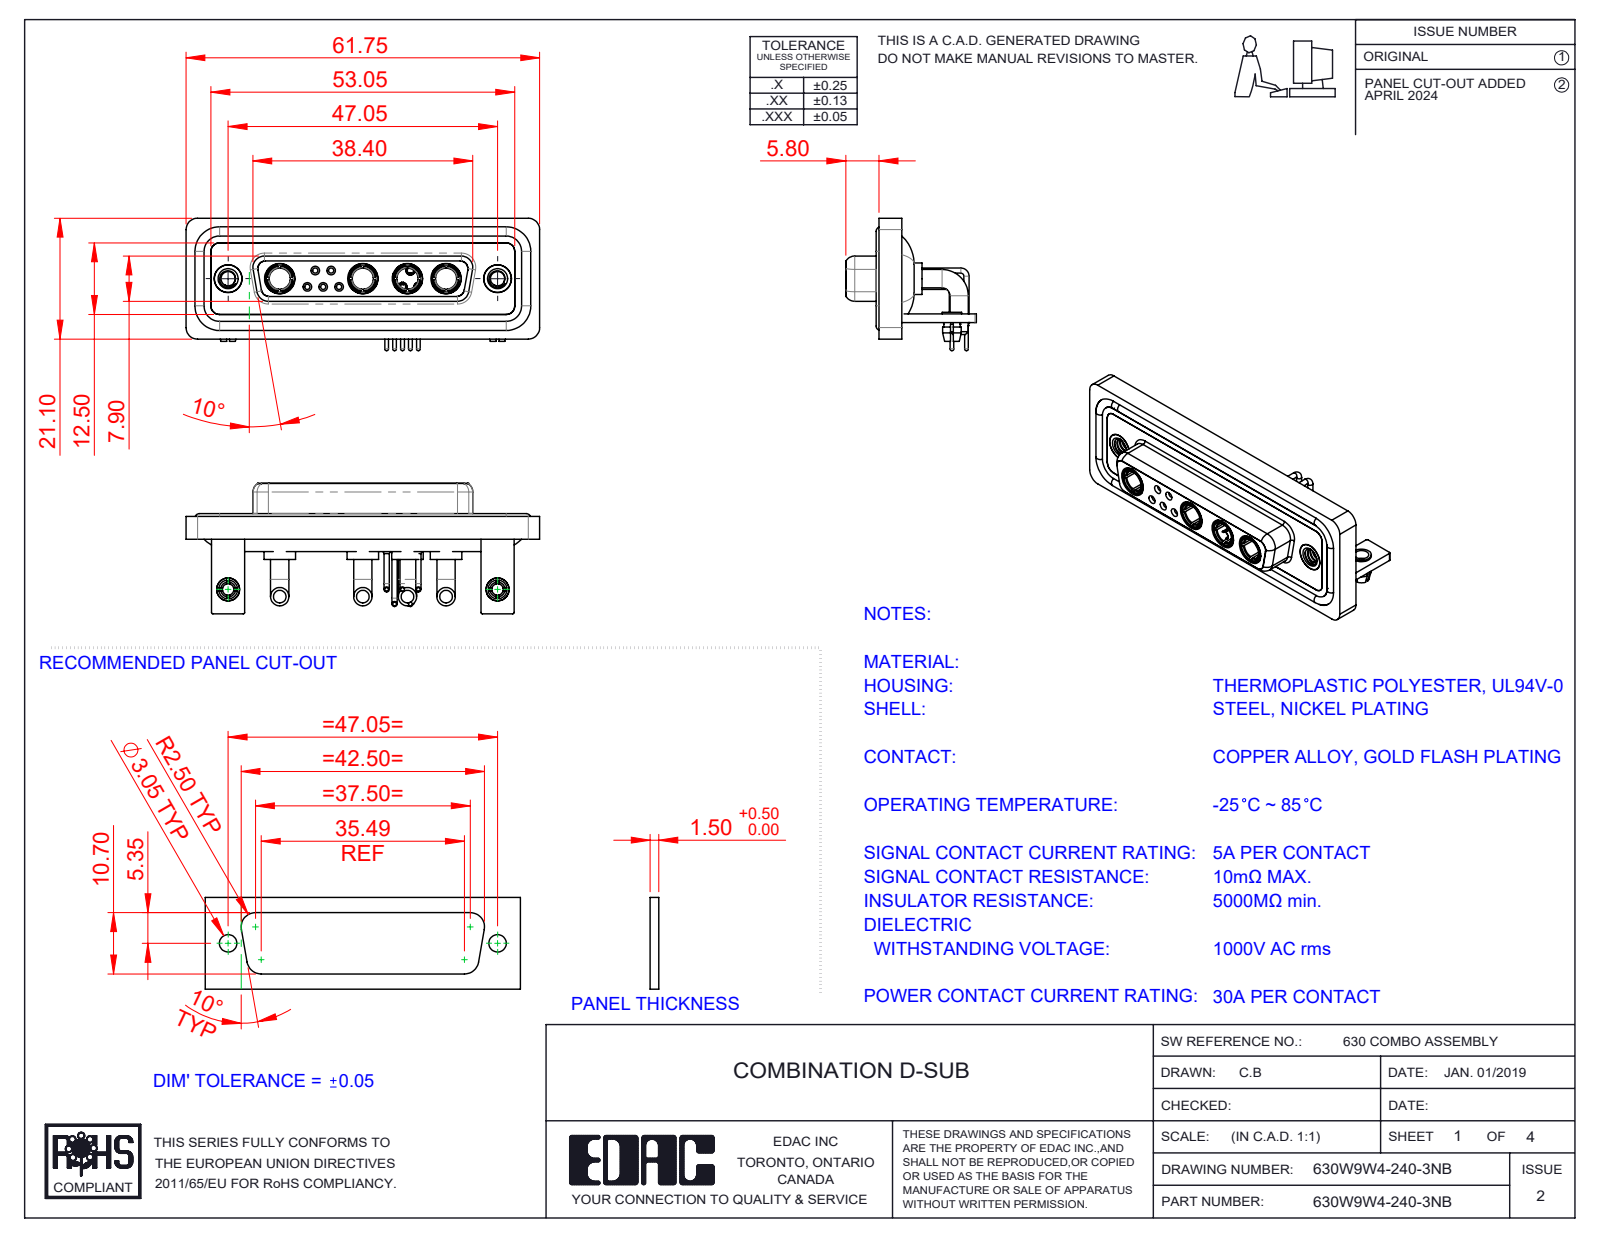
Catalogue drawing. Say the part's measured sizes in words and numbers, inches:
The part is named "Power Socket_30A RA; 630Combo Stabilizer Bracket_50 Contacts; 630Combo Shell Rear_25 Contacts; 630Combo Board Lock_50 Contacts (+7 more)". Its 3-D file was written by "SolidWorks 2023 (CONFIG_CONTROL_DESIGN)". It is 24 solids with 1097 faces: 364 planar, 457 cylindrical and 276 other. Overall it measures 2.431 by 0.91 by 0.898 inches. Its volume is 0.547 cubic inches and its surface area 23.36 square inches. Round holes: 7 of diameter 0.079, 6 of diameter 0.191, 5 of diameter 0.035, 5 of diameter 0.043, 5 of diameter 0.059, 4 of diameter 0.098, 4 of diameter 0.146, 4 of diameter 0.209, 3 of diameter 0.063, 2 of diameter 0.067, 2 of diameter 0.126, 2 of diameter 0.157. Round bosses or shafts: 10 of diameter 0.035, 9 of diameter 0.063, 8 of diameter 0.126, 5 of diameter 0.079, 5 of diameter 0.059, 5 of diameter 0.026, 4 of diameter 0.217, 4 of diameter 0.205. Partial cylindrical surfaces (rounded edges, fillets, slot ends): 19 of radius 0.079, 18 of radius 0.059, 16 of radius 0.01, 8 of radius 0.053, 8 of radius 0.063, 5 of radius 0.02, 4 of radius 0.024, 4 of radius 0.026. The main face-to-face distances are 0.016, 0.071, 0.114, 0.146, 0.059, 0.161, 0.043, 0.055, 0.063, 0.098. The hole center spacings are 0.124, 0.109, 0.198, 0.545, 0.436, 0.504, 0.61, 0.218.
